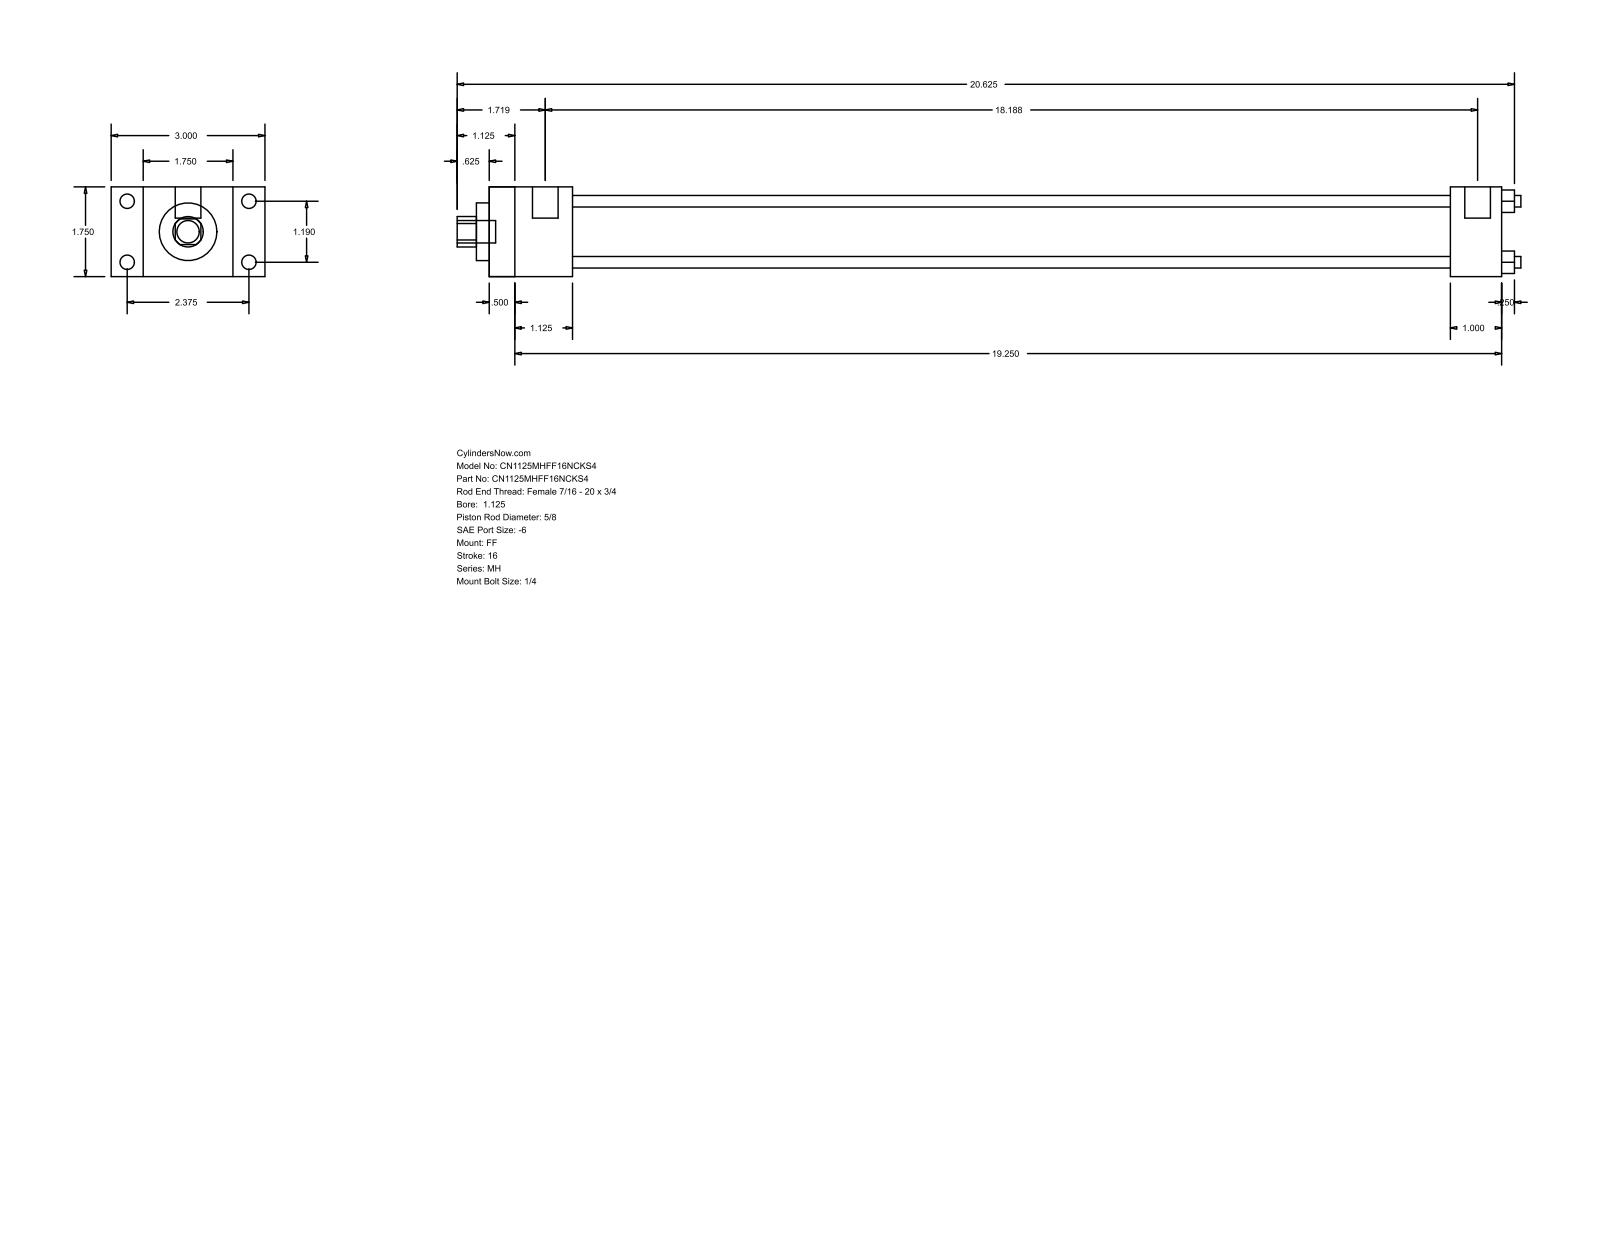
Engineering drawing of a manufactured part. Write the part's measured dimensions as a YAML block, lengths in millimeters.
part_name: "MH_FF__0112_0.625"
step_written_by: "GSSL Pune (CONFIG_CONTROL_DESIGN)"
units: millimeters
bodies: {solids: 0, faces: 92, planar: 64, cylindrical: 28, other: 0}
overall_size: [527.05, 76.2, 44.45]
round_holes:
  - {diameter: 5.71, count: 4}
  - {diameter: 15.88, count: 1}
  - {diameter: 28.57, count: 1}
  - {diameter: 34.92, count: 1}
round_bosses_or_shafts:
  - {diameter: 7.14, count: 4}
  - {diameter: 5.56, count: 4}
  - {diameter: 12.7, count: 2}
  - {diameter: 11.11, count: 1}
partial_cylinders:
  - {radius: 7.54, count: 1}
face_to_face_distances: [44.46, 501.64, 15.87, 12.69, 488.95, 60.33, 28.58, 41.27, 476.24, 463.55]
hole_center_spacings: [21.37, 30.22, 42.74]
